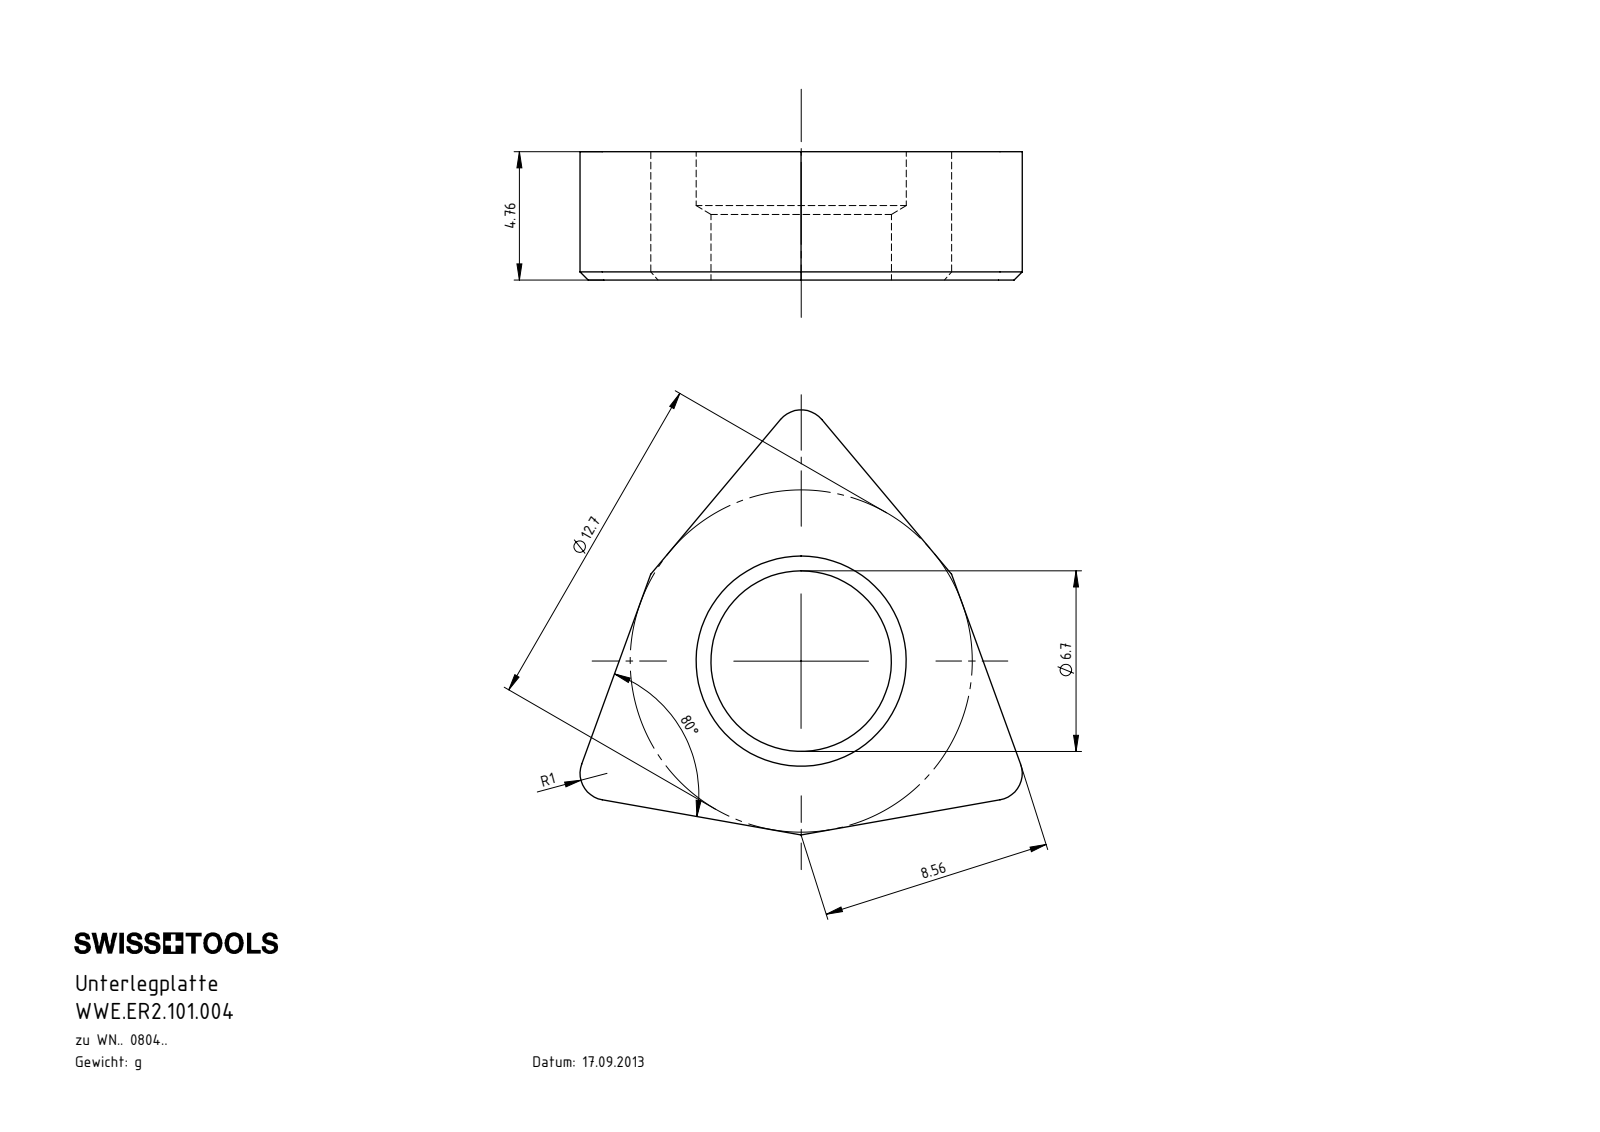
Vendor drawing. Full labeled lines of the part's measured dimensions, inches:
Part name (STEP PRODUCT): WWE.ER2.101.004
STEP written by: SolidWorks 2017 (AUTOMOTIVE_DESIGN)
Units: inches
Bodies: 1 solid, 23 faces (14 planar, 5 cylindrical, 4 other)
Overall size (bounding box): 0.646 × 0.621 × 0.187
Volume: 0.036 in³ · Surface area: 0.916 in²
Round holes (diameter × count): ⌀0.264 ×1, ⌀0.307 ×1
Partial cylindrical surfaces — rounded edges, fillets, slot ends (radius × count): R0.039 ×3
Main face-to-face distances: 0.187
